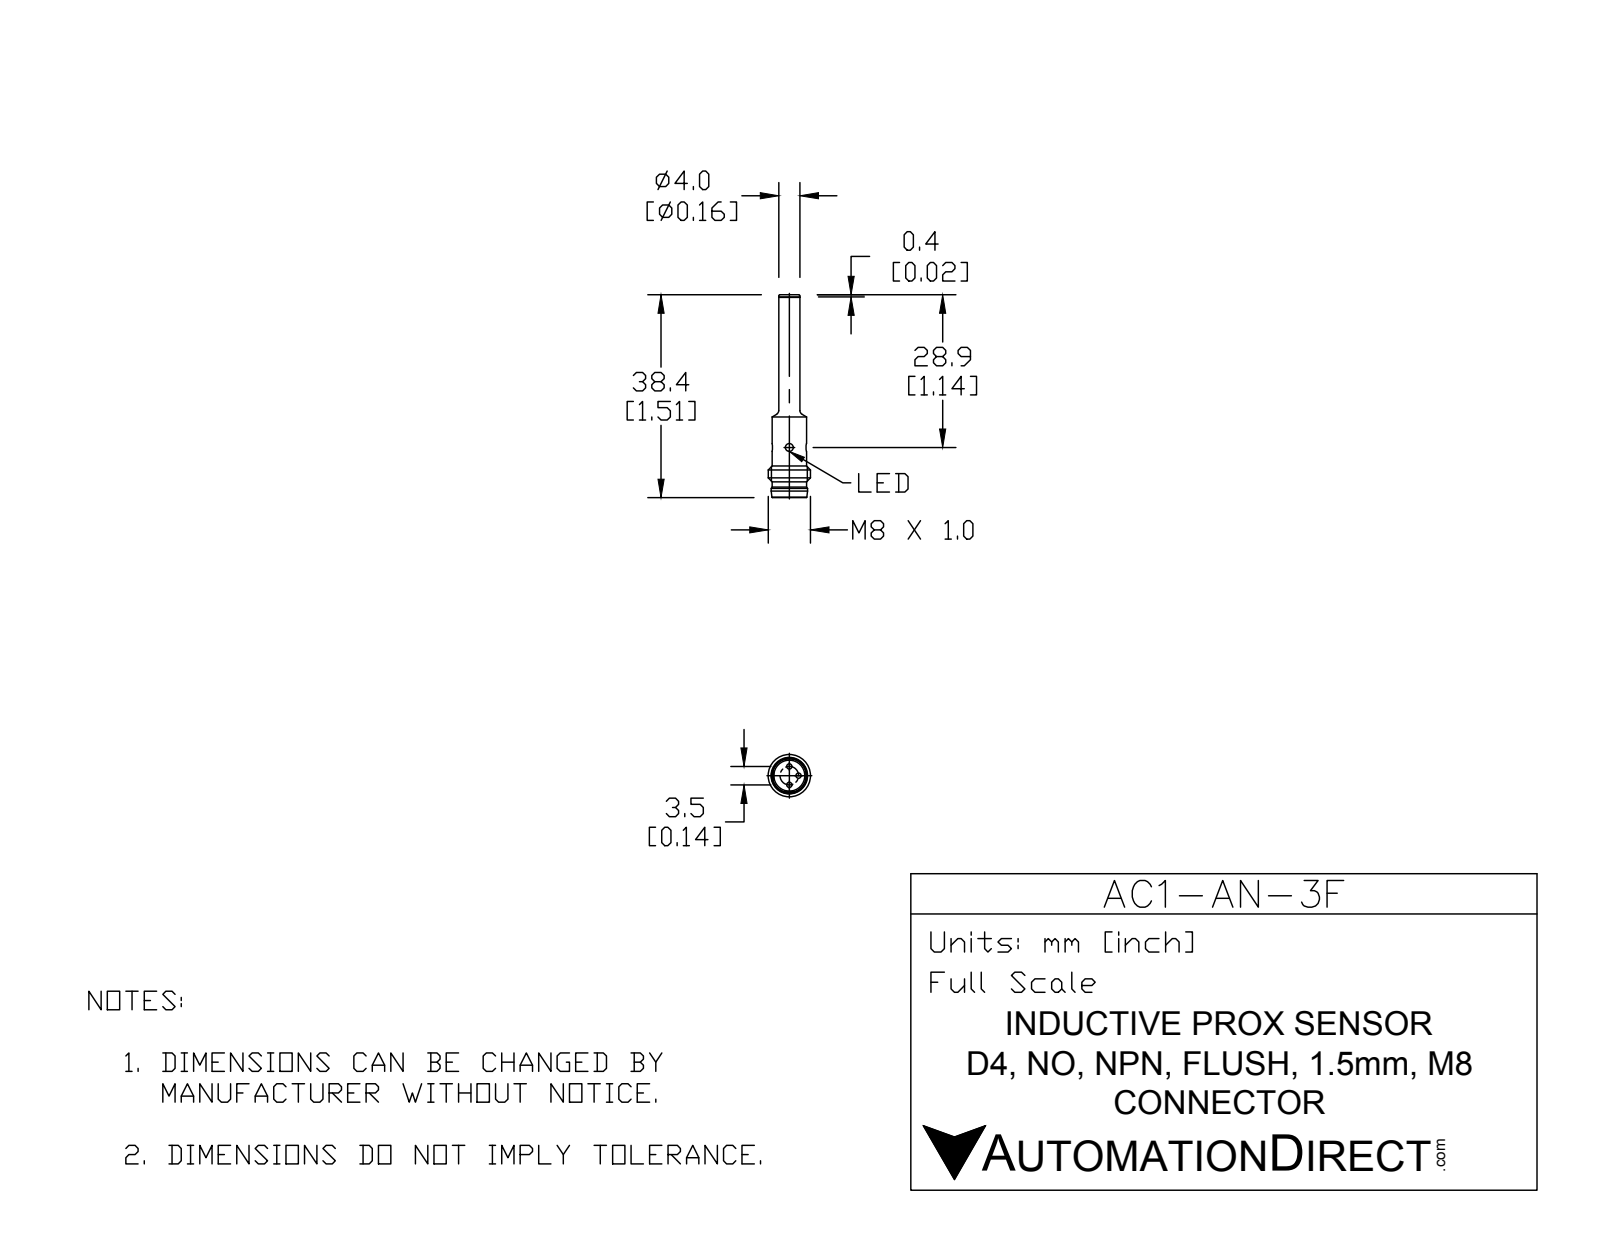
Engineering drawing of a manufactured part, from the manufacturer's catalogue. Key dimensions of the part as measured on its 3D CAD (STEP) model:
Part name (STEP PRODUCT): AC1-AN-3F
STEP written by: SolidWorks 2015 (CONFIG_CONTROL_DESIGN)
Units: millimetres
Bodies: 4 solids, 59 faces (11 planar, 26 cylindrical, 22 other)
Overall size (bounding box): 38.4 × 8 × 8
Volume: 757 mm³ · Surface area: 840 mm²
Round holes (diameter × count): ⌀1.5 ×2, ⌀5.85 ×1
Round bosses / shafts (diameter × count): ⌀1 ×3, ⌀8 ×1, ⌀6.9 ×1, ⌀6.5 ×1, ⌀4 ×1
Main face-to-face distances: 33.4, 5.5, 5, 38.4, 38, 33, 0.4
